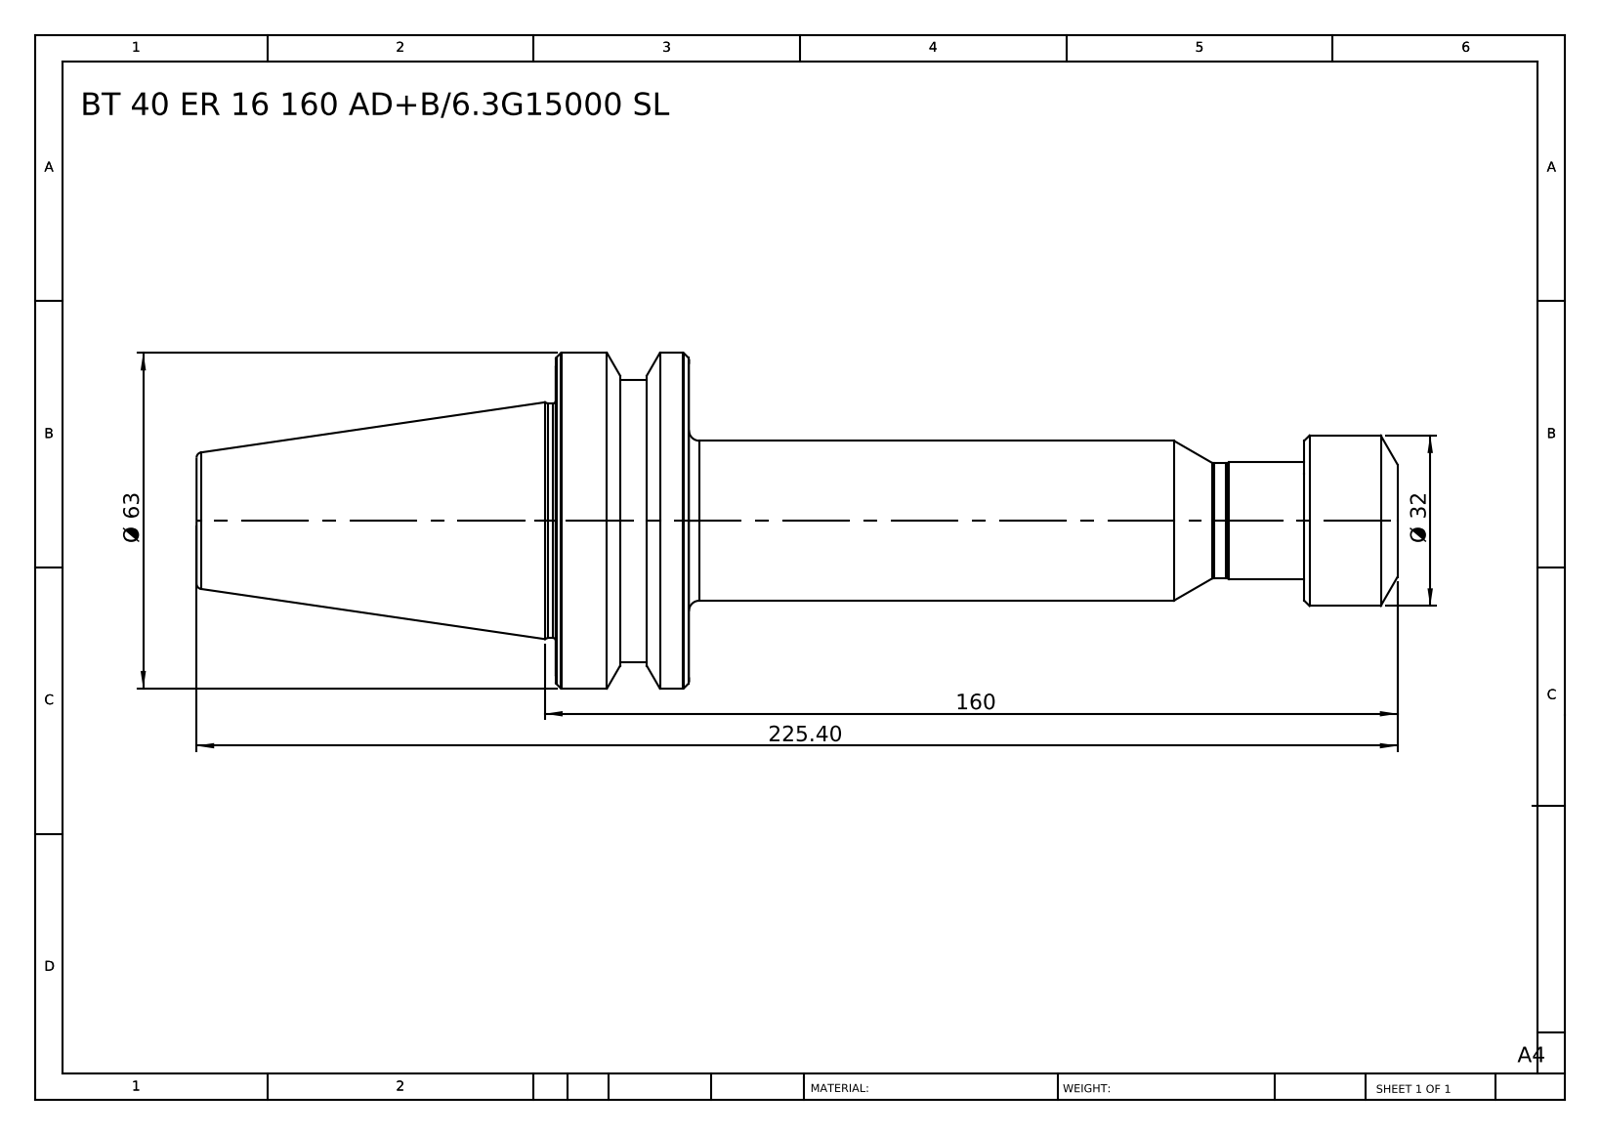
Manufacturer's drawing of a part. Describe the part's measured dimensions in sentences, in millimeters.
The part is named "BT40 ER 16 160 AD-6.3G15000 SL". Its 3-D file was written by "SolidWorks 2014 (CONFIG_CONTROL_DESIGN)". It is 1 solid with 69 faces: 7 planar, 16 cylindrical and 46 other. Overall it measures 225.4 by 63 by 63 millimeters. Its volume is 226 415 cubic millimeters and its surface area 30 695 square millimeters. Round bosses or shafts: 1 of diameter 63, 1 of diameter 53, 1 of diameter 44, 1 of diameter 32, 1 of diameter 30, 1 of diameter 21.9, 1 of diameter 21.5. The main face-to-face distances are 25, 92.4, 67.4, 133, 158, 225.4, 17.5, 115.5, 140.5, 207.9.
